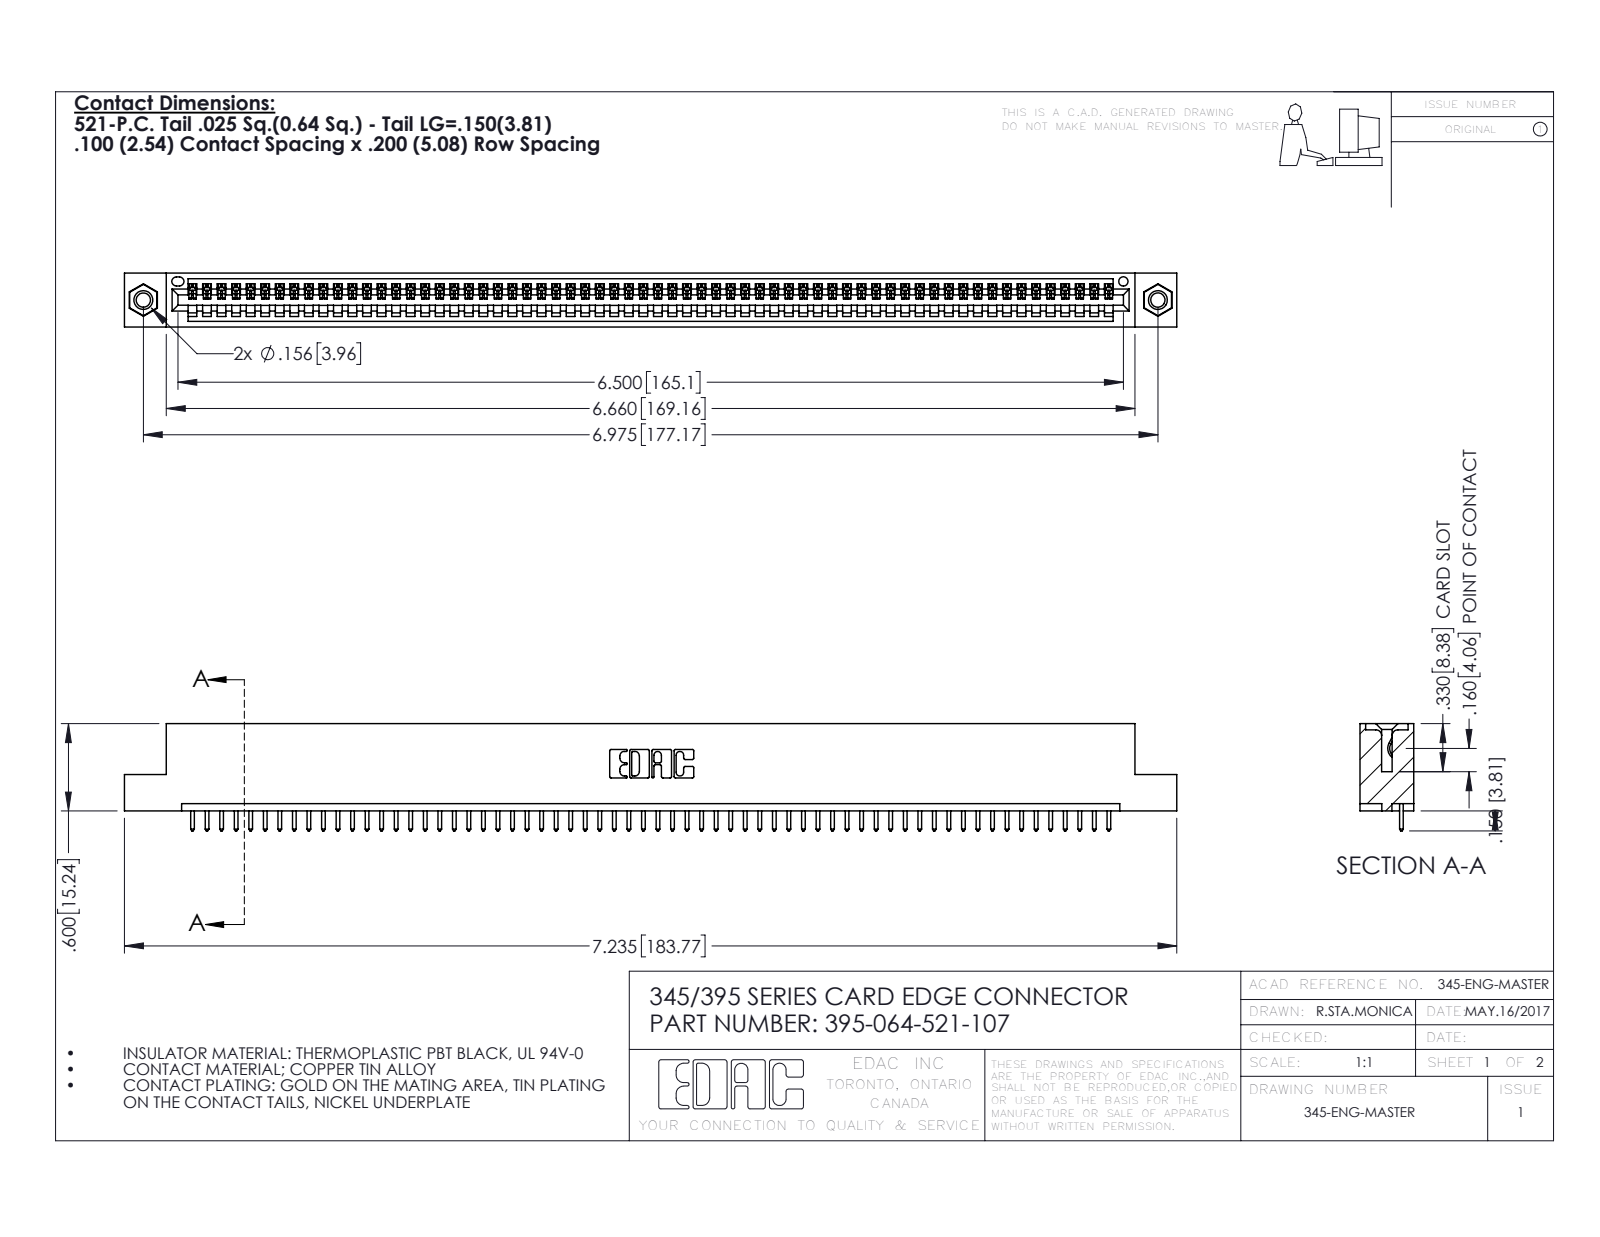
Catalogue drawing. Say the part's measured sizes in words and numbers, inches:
The part is named "395-064-521-107; 345-250-001_345-250-005-103; 345 Part_Flush Mounting Lugs - 0.156 Dia-TI; 345-292-001_345-293-121". Its 3-D file was written by "SolidWorks 2016 (CONFIG_CONTROL_DESIGN)". It is 67 solids with 3898 faces: 2672 planar, 1210 cylindrical and 16 other. Overall it measures 7.235 by 0.737 by 0.37 inches. Its volume is 1.064 cubic inches and its surface area 35.33 square inches. Round holes: 2 of diameter 0.098, 2 of diameter 0.125, 2 of diameter 0.156, 1 of diameter 0.064. Round bosses or shafts: 2 of diameter 0.155. Partial cylindrical surfaces (rounded edges, fillets, slot ends): 128 of radius 0.006, 128 of radius 0.01, 22 of radius 0.01, 6 of radius 0.007, 6 of radius 0.031, 3 of radius 0.026, 2 of radius 0.031, 2 of radius 0.04. The main face-to-face distances are 0.072, 0.298, 0.37, 0.2, 0.098, 0.272, 0.025, 0.225, 0.149, 0.072. The hole center spacings are 0.27, 6.739, 6.975.
